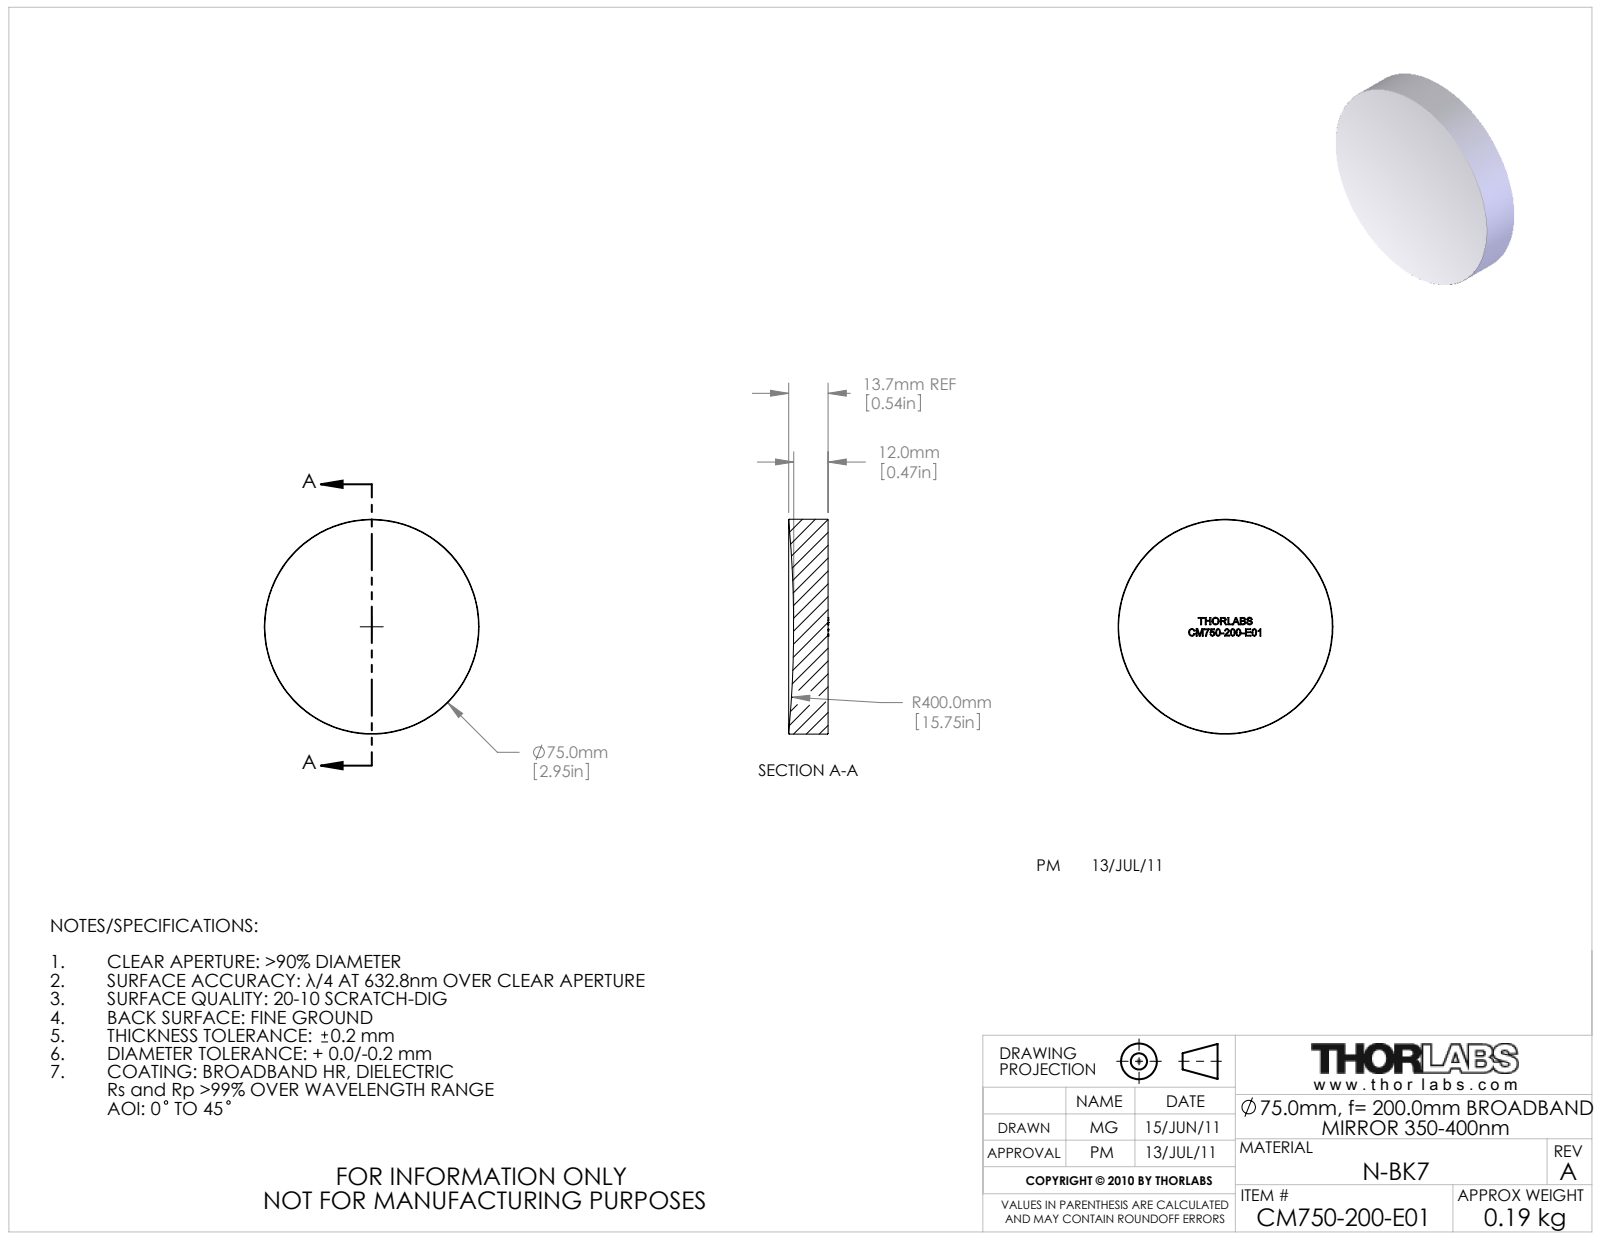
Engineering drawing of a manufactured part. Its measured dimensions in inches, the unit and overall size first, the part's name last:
Units: inches
Overall size (bounding box): 2.953 × 2.953 × 0.541
Round bosses / shafts (diameter × count): ⌀2.953 ×1
Bodies: 0 solids, 42 faces (32 planar, 2 cylindrical, 8 other)
Part name (STEP PRODUCT): 22621-E0W
STEP written by: SolidWorks 2011 (AUTOMOTIVE_DESIGN)
